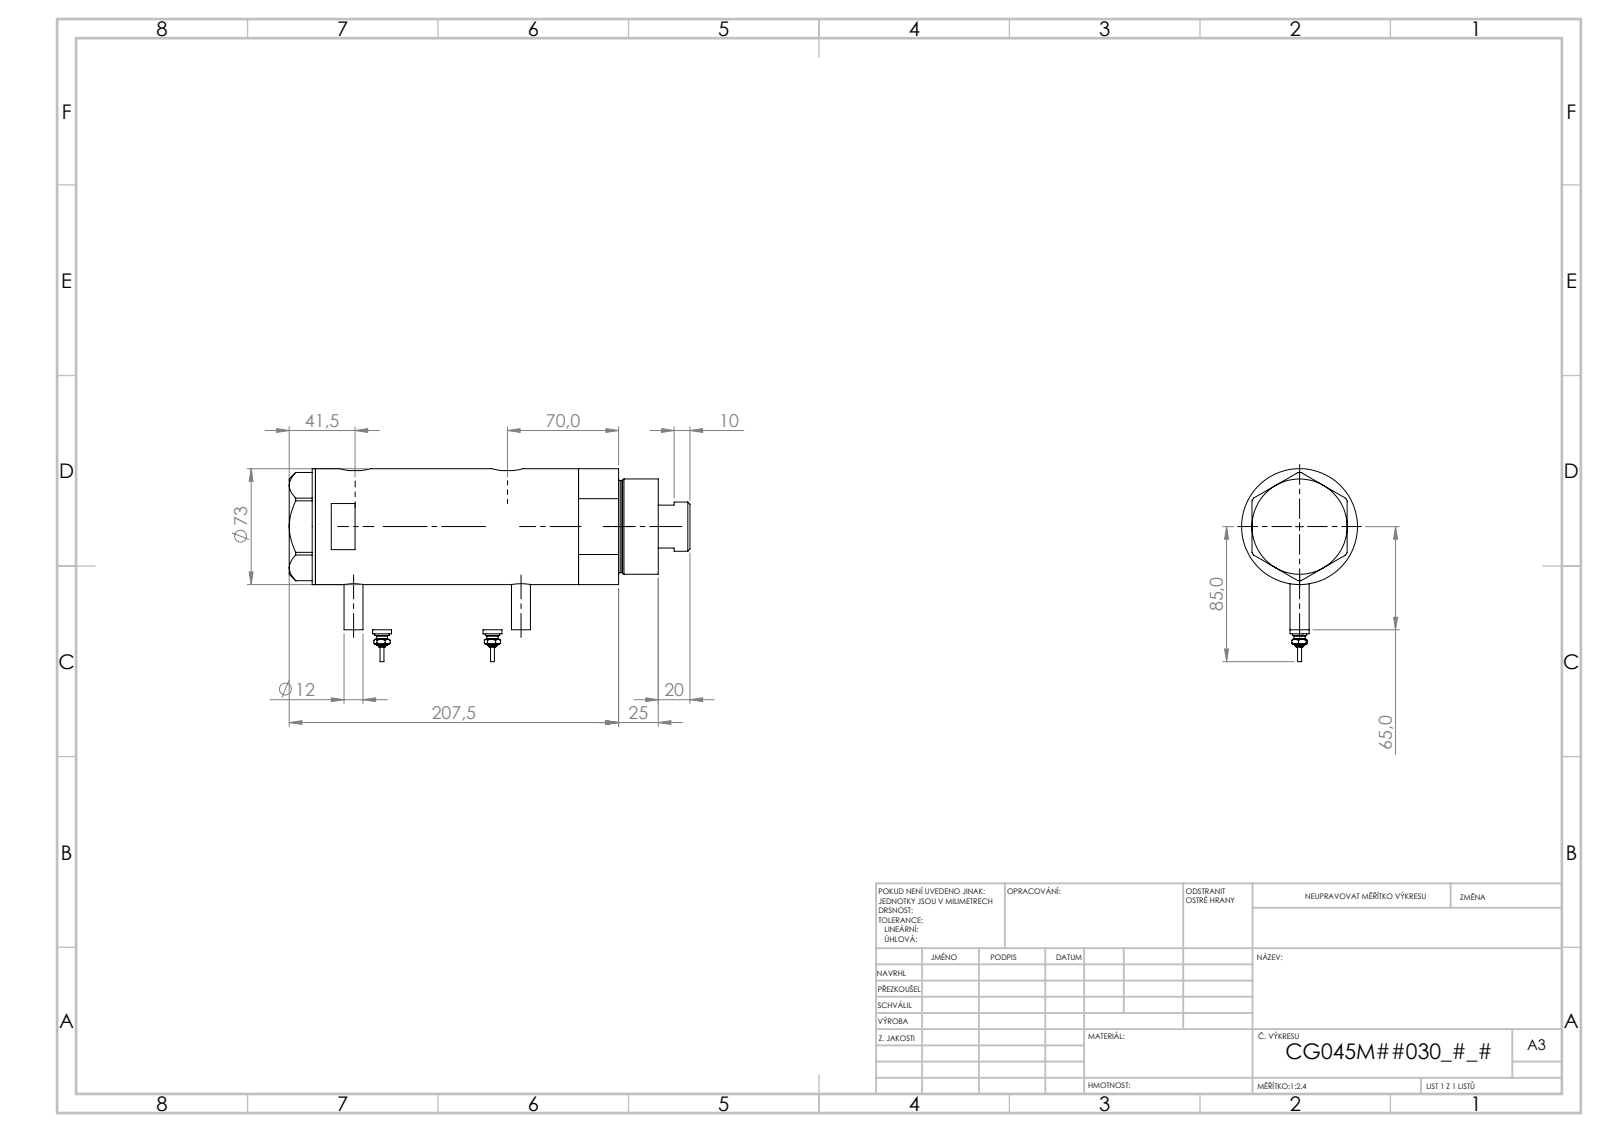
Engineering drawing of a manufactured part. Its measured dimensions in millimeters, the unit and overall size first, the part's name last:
Units: millimetres
Overall size (bounding box): 221.52 × 105.3 × 73
Round holes (diameter × count): ⌀5 ×2, ⌀12.5 ×2, ⌀13.16 ×2, ⌀10.5 ×1, ⌀32 ×1, ⌀33.5 ×1, ⌀45 ×1, ⌀48 ×1, ⌀64 ×1
Round bosses / shafts (diameter × count): ⌀12 ×3, ⌀9 ×2, ⌀7 ×2, ⌀4.34 ×2, ⌀2.4 ×2, ⌀73 ×1, ⌀60 ×1, ⌀58 ×1
Partial cylindrical surfaces — rounded edges, fillets, slot ends (radius × count): R10 ×2
Main face-to-face distances: 97.14, 16.5, 113.64, 185.01, 201.51, 87.87, 42.5, 26, 71.14, 159.01
Hole centre spacings: 81.65, 0.99, 1, 8.5, 8.51, 72.15, 73.14, 73.15
Volume: 771 588 mm³ · Surface area: 136 024 mm²
Bodies: 6 solids, 231 faces (78 planar, 79 cylindrical, 74 other)
Part name (STEP PRODUCT): V270CG_FRONT; V270CG_VC; V270CG_BACK; V270CG_MIDDLE (+1 more)
STEP written by: SolidWorks 2019 (CONFIG_CONTROL_DESIGN)
